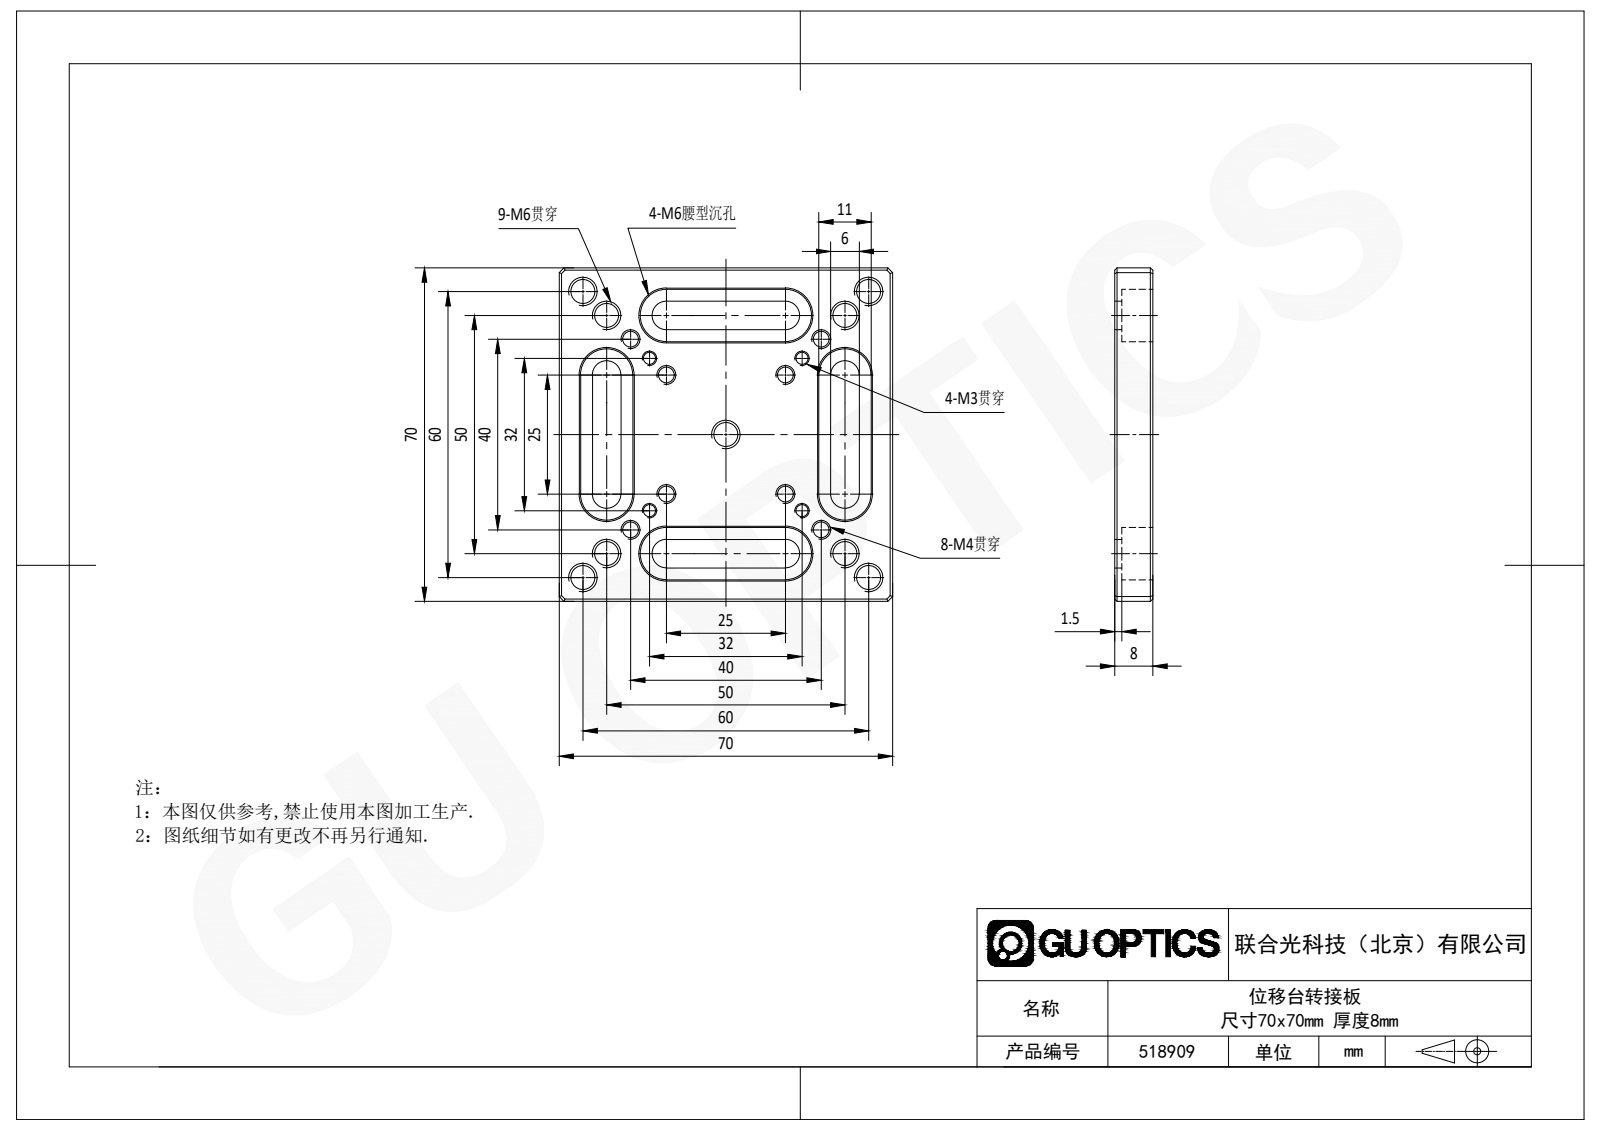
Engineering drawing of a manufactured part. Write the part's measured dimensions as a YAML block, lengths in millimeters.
step_written_by: "SolidWorks 2020 (CONFIG_CONTROL_DESIGN)"
units: millimeters
bodies: {solids: 1, faces: 120, planar: 54, cylindrical: 37, other: 29}
overall_size: [70, 70, 8]
volume: 26267
surface_area: 14445
round_holes:
  - {diameter: 5, count: 9}
  - {diameter: 3.3, count: 8}
  - {diameter: 2.5, count: 4}
partial_cylinders:
  - {radius: 3, count: 8}
  - {radius: 5.5, count: 8}
face_to_face_distances: [8, 70, 50, 1.5, 6.5, 4.5, 15.5, 54.5, 65.5, 11]
hole_center_spacings: [45.96, 7.07, 17.68, 28.71, 33.35, 36.22, 39.53, 41.98]
